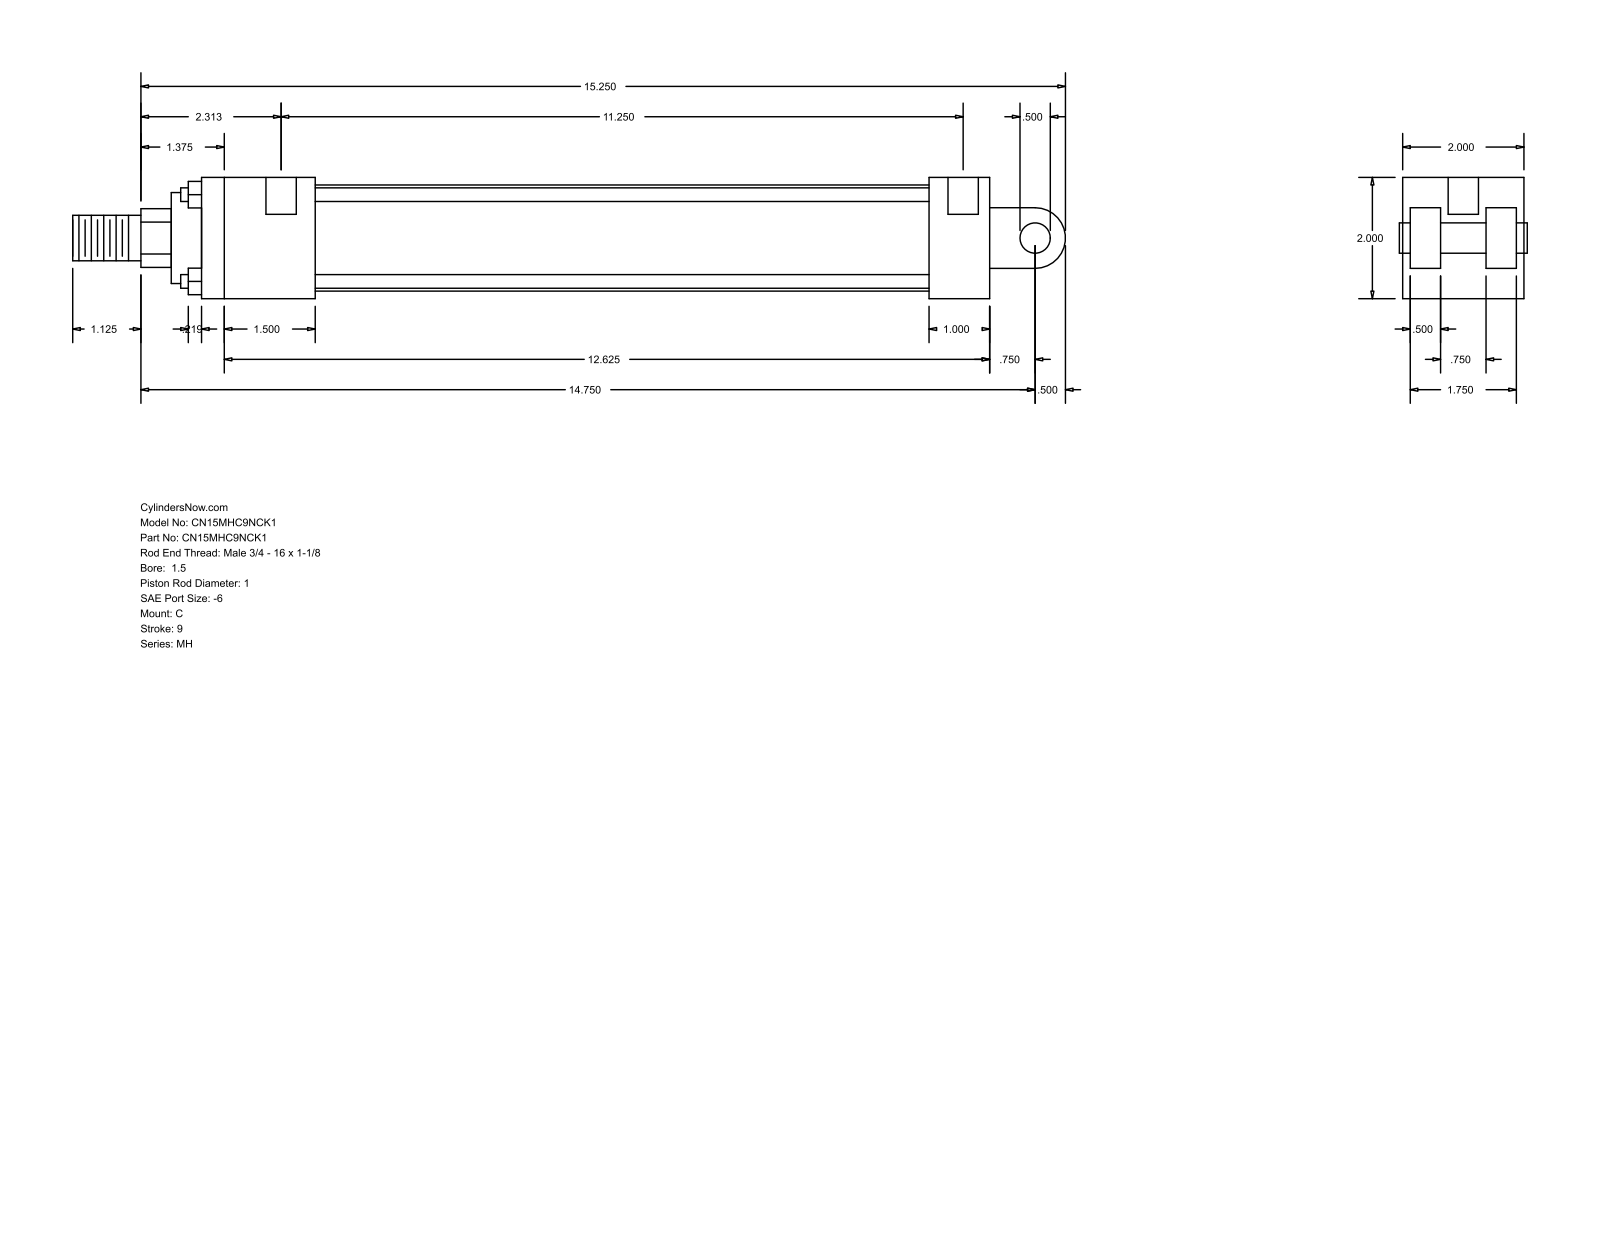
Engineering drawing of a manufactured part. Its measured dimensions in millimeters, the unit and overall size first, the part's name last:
Units: millimetres
Overall size (bounding box): 415.93 × 50.8 × 50.8
Round holes (diameter × count): ⌀5.56 ×4, ⌀12.7 ×2
Round bosses / shafts (diameter × count): ⌀5.71 ×4, ⌀44.45 ×1, ⌀38.1 ×1, ⌀25.4 ×1, ⌀19.05 ×1, ⌀12.7 ×1
Partial cylindrical surfaces — rounded edges, fillets, slot ends (radius × count): R12.29 ×1, R12.7 ×1
Main face-to-face distances: 50.8, 12.7, 47.63, 25.4, 3.17, 15.87, 34.93, 31.76, 330.2, 38.1
Hole centre spacings: 288.93, 3.18, 285.75
Bodies: 0 solids, 99 faces (70 planar, 29 cylindrical, 0 other)
Part name (STEP PRODUCT): MH_C__0150_1
STEP written by: GSSL Pune (CONFIG_CONTROL_DESIGN)
